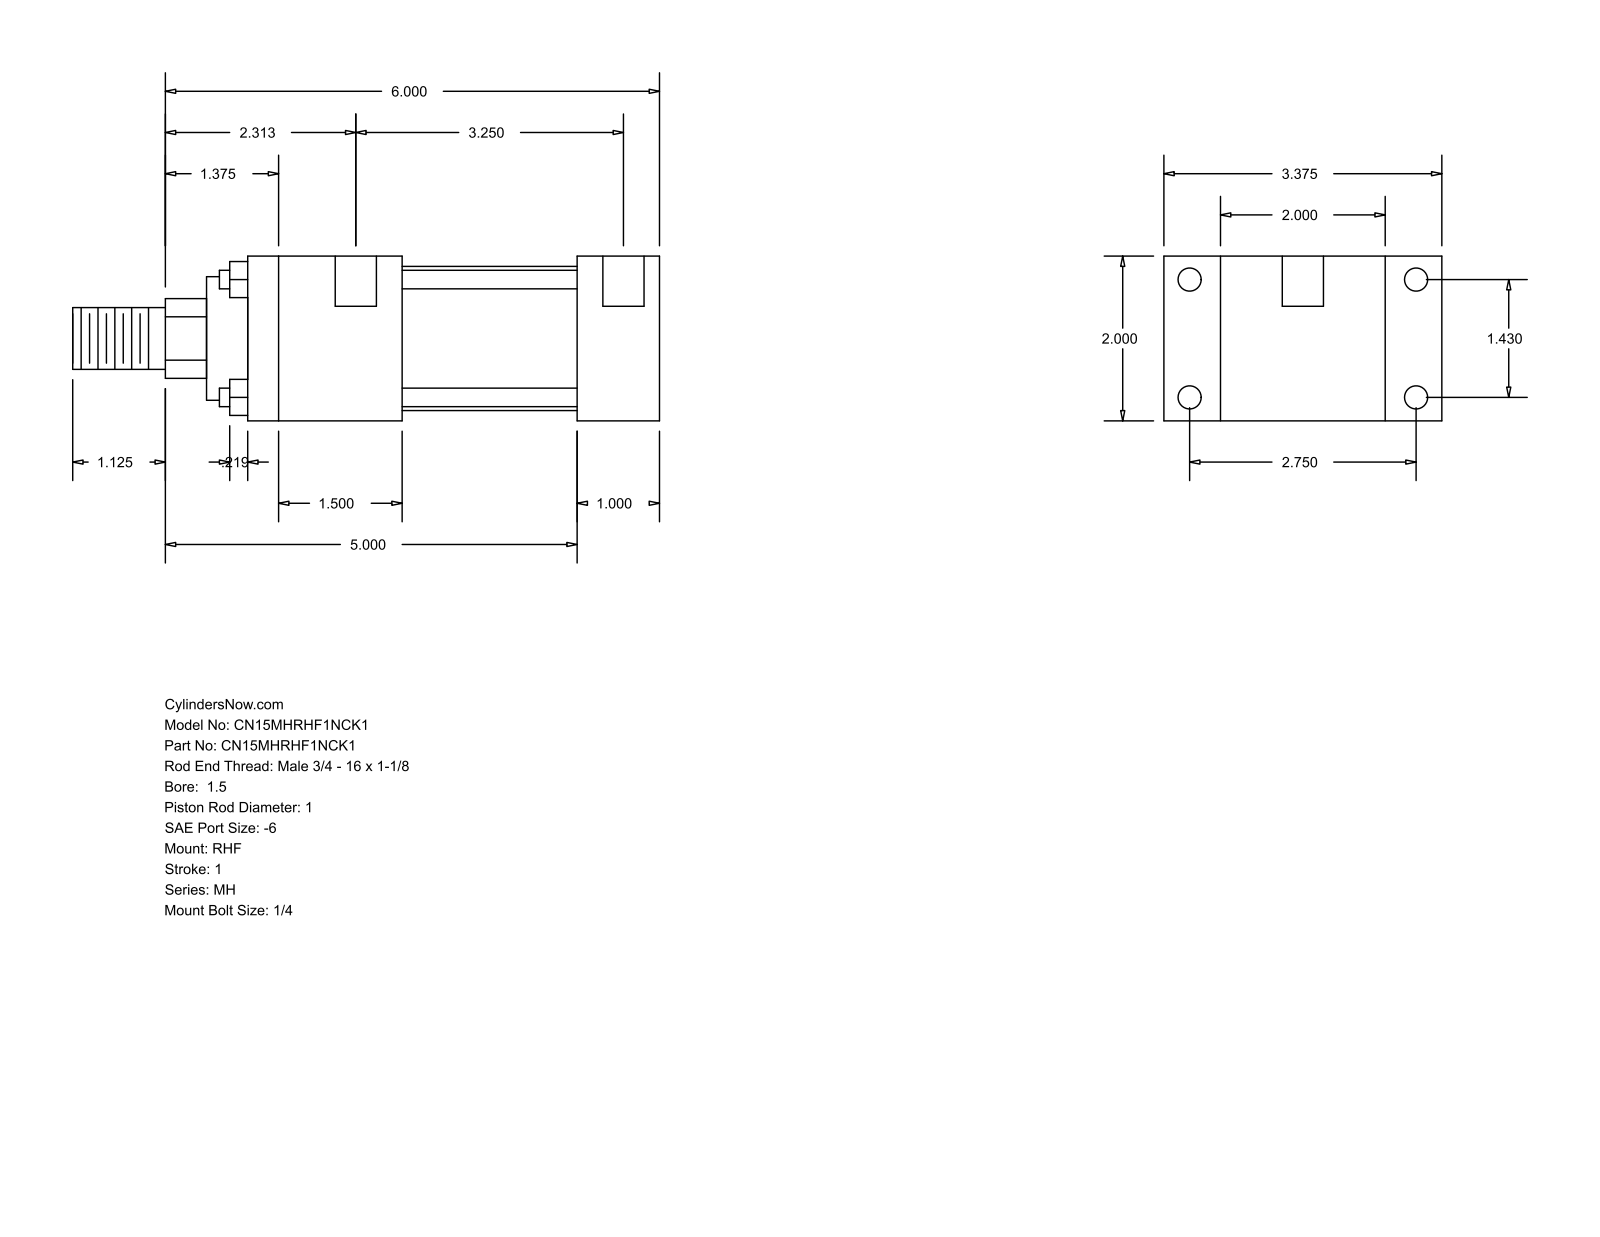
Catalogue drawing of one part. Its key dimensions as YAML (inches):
part_name: "MH_RHF__0150_1"
step_written_by: "GSSL Pune (CONFIG_CONTROL_DESIGN)"
units: inches
bodies: {solids: 0, faces: 88, planar: 60, cylindrical: 28, other: 0}
overall_size: [7.125, 3.375, 2]
round_holes:
  - {diameter: 0.219, count: 4}
  - {diameter: 0.281, count: 4}
  - {diameter: 0.5, count: 2}
round_bosses_or_shafts:
  - {diameter: 0.225, count: 4}
  - {diameter: 1.75, count: 1}
  - {diameter: 1.5, count: 1}
  - {diameter: 1, count: 1}
  - {diameter: 0.75, count: 1}
partial_cylinders:
  - {radius: 0.484, count: 1}
face_to_face_distances: [2, 1, 0.687, 2.687, 4, 3.375, 2.125, 5, 1.875, 3.125]
hole_center_spacings: [1.43, 2.75, 3.099, 3.375, 0.125, 3.25]
